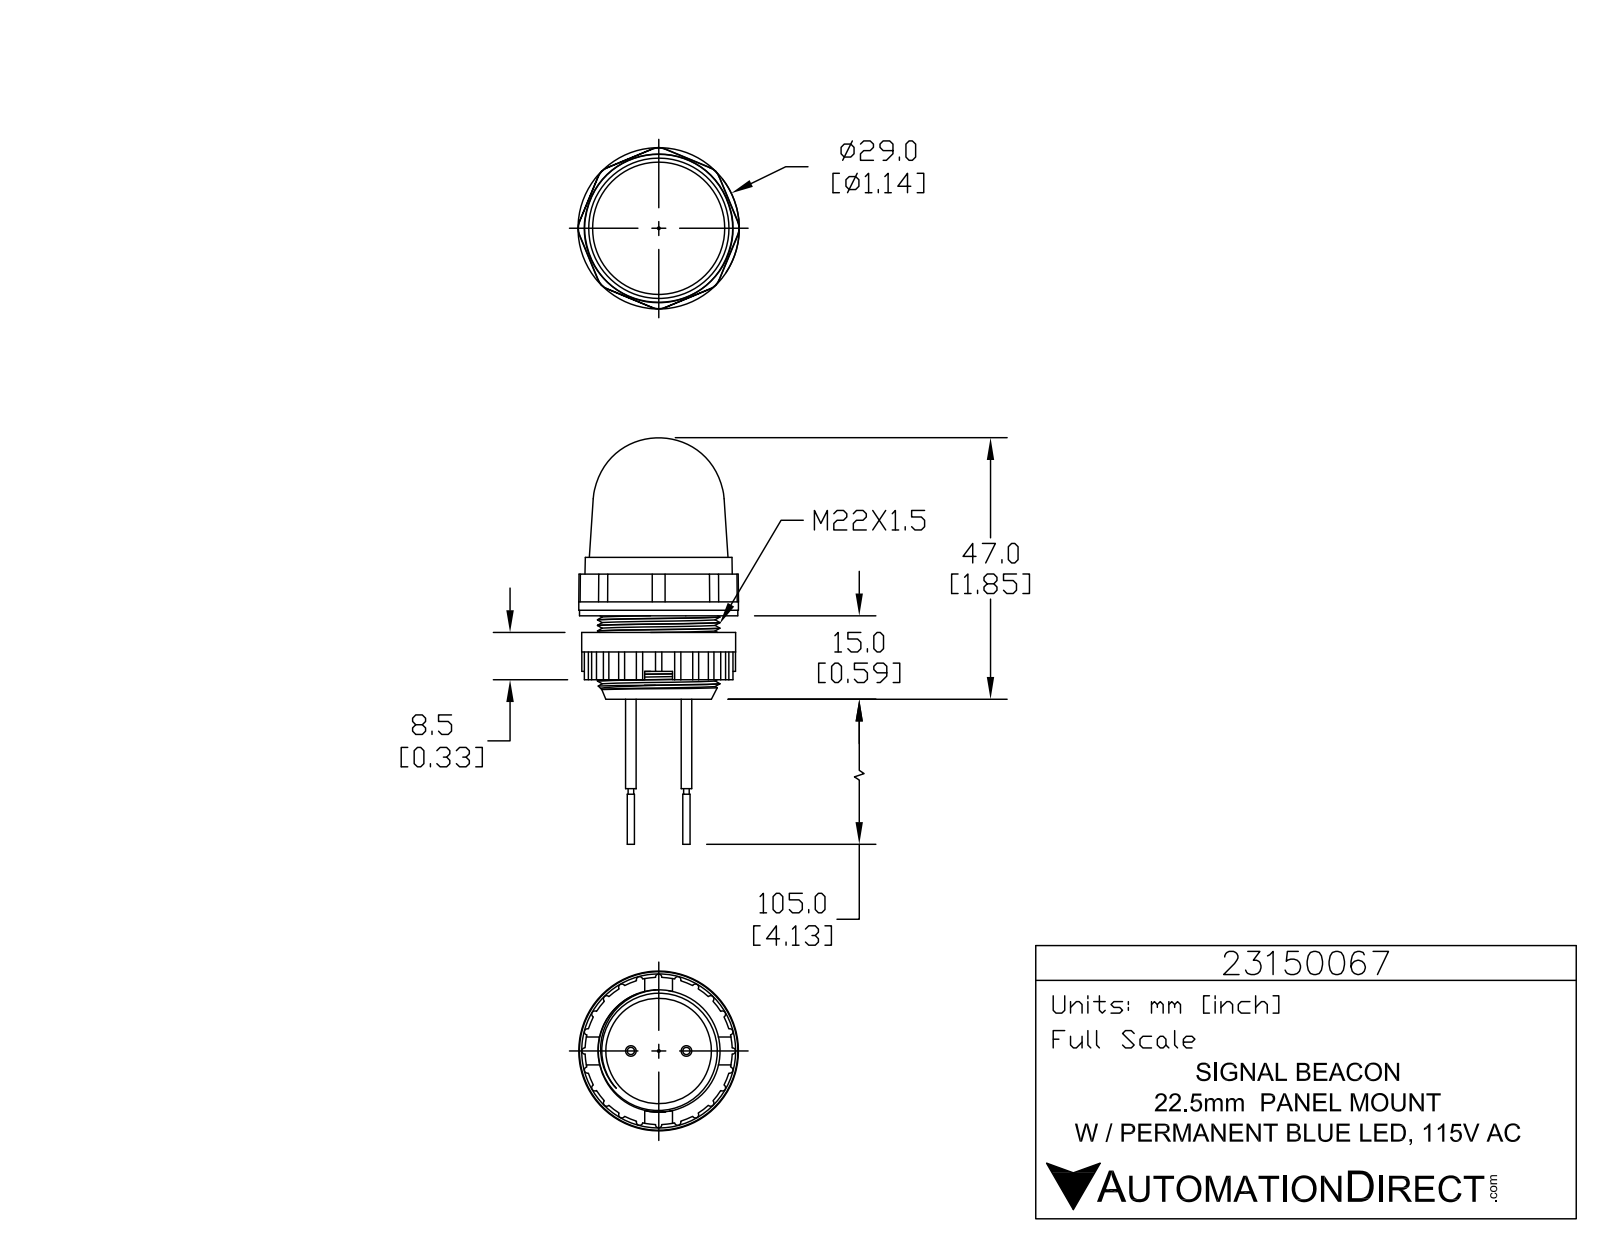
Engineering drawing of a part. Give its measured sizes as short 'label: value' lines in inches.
name: 23150067
written by: SolidWorks 2017 (AUTOMOTIVE_DESIGN)
unit: in
bodies: 1 solid, 934 faces (568 planar, 269 cylindrical, 97 other)
size: 2.82 × 1.131 × 1.131
volume: 1.255 in³; area: 12.16 in²
holes: 3× ⌀0.02
bosses: 3× ⌀0.113, 3× ⌀0.028, 2× ⌀0.075, 2× ⌀0.051, 2× ⌀0.039, 1× ⌀1.131, 1× ⌀1.122, 1× ⌀1.091
rounds: 24× R0.023, 8× R0.118, 6× R0.004, 6× R0.004, 6× R0.004, 6× R0.065, 3× R0.005, 3× R0.007
face distances: 0.551, 0.118, 0.433, 0.098, 0.335, 0.453, 0.492, 0.413, 0.295, 0.197
